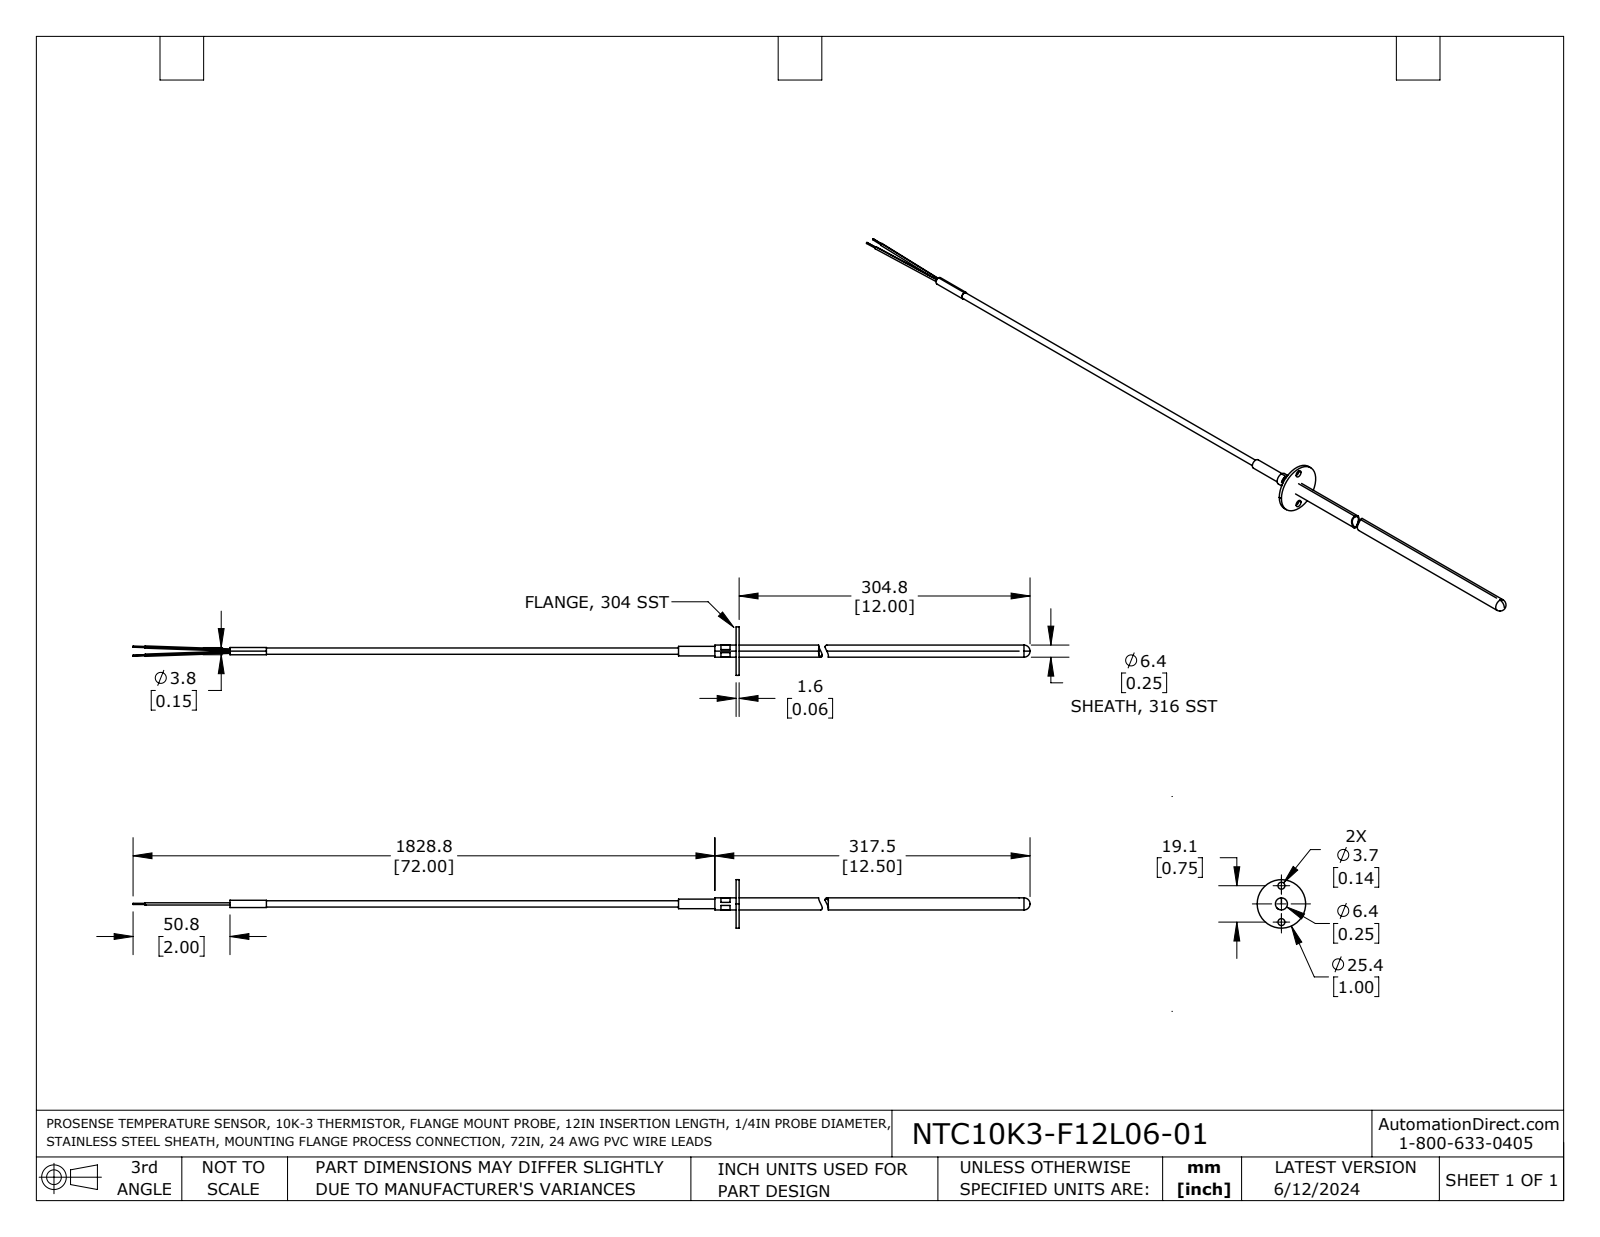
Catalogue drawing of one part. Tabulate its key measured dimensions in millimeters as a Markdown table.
| quantity | value |
| --- | --- |
| part name | NTC10K3-F12L06-0 |
| STEP written by | SolidWorks 2021 (AUTOMOTIVE_DESIGN) |
| units | millimeters |
| bodies | 4 solids, 59 faces (27 planar, 22 cylindrical, 10 other) |
| overall size | 622.3 × 25.4 × 25.4 |
| volume | 6 180 mm³ |
| surface area | 17 330 mm² |
| round holes (diameter × count) | 3.7 × 2, 3.3 × 1, 4.7 × 1, 4.9 × 1, 5.3 × 1 |
| round bosses / shafts (diameter × count) | 25.4 × 1, 6.4 × 1, 5 × 1, 3.8 × 1, 3.3 × 1 |
| main face-to-face distances | 1.6, 5.5, 300.7, 299.1, 11.1, 12.7, 311.8, 8, 254, 265.2 |
| hole center spacings | 9.5, 19.1 |
